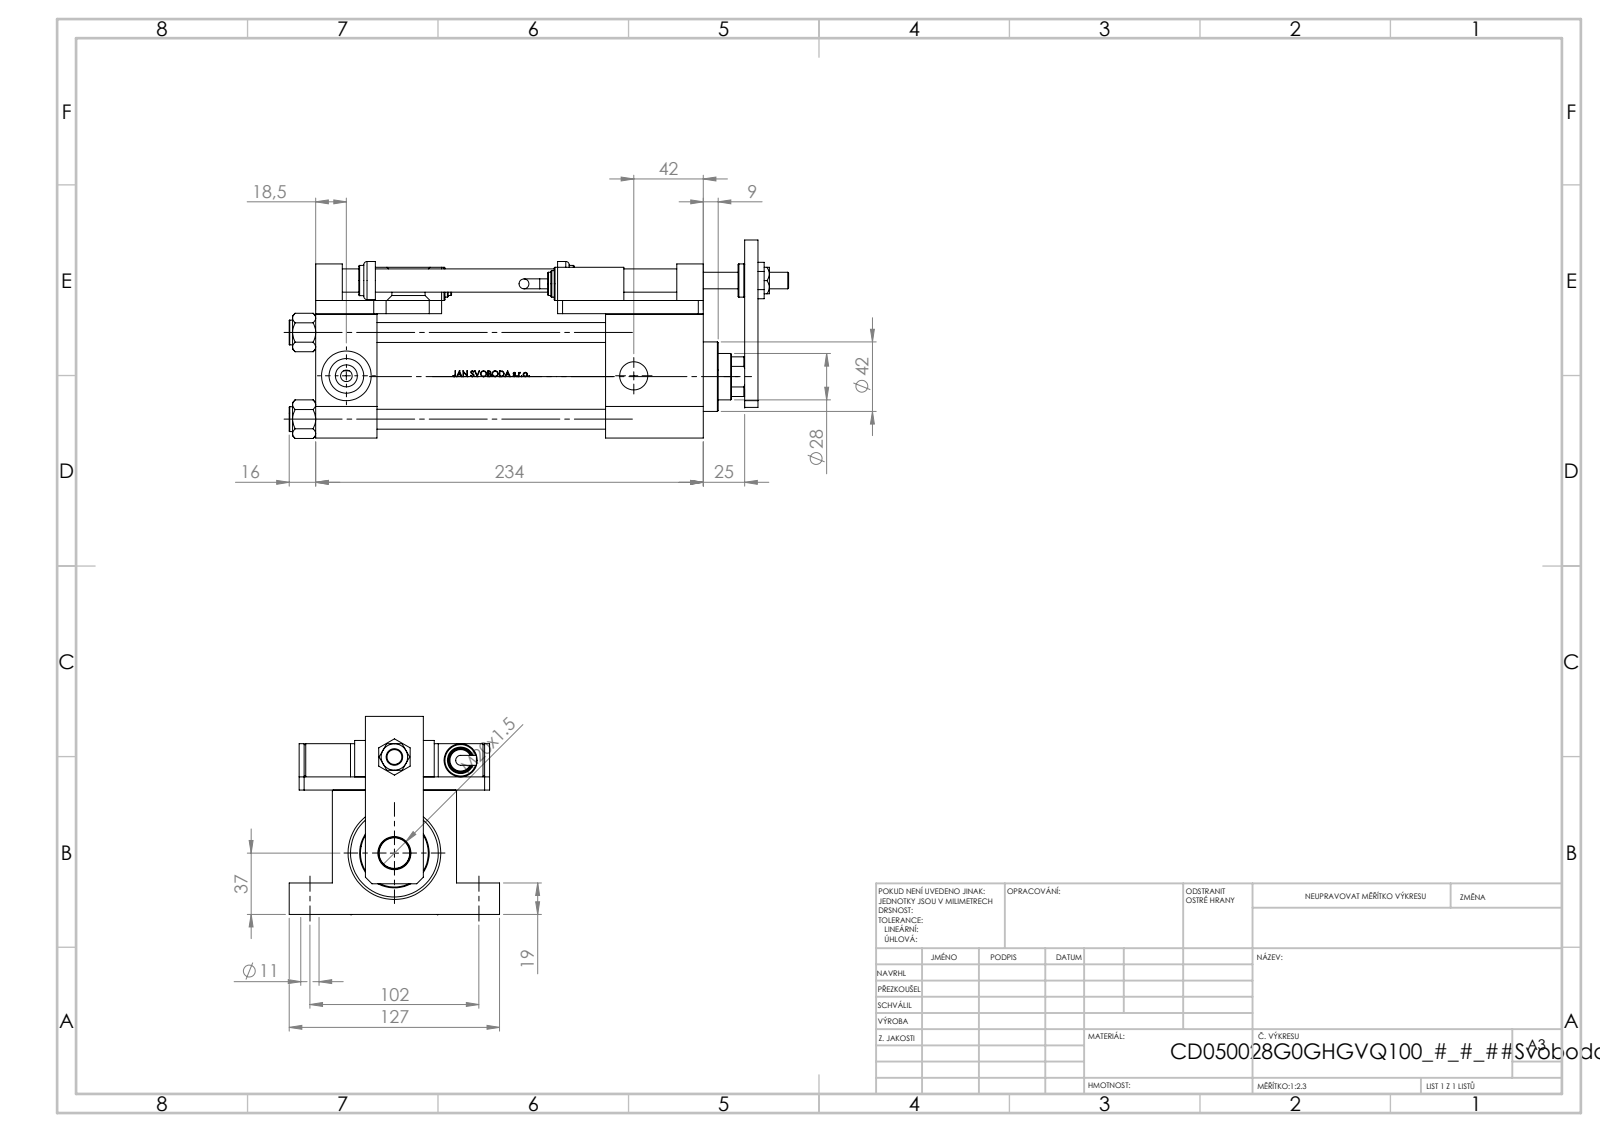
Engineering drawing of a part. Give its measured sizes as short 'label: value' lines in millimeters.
name: V215CD_SWITCH_Q_PODLOZKA_BACK; V215CD_SWITCH_Q_DIMA; V215CD_SWITCH_Q_SWITCH; V215CD_SWITCH_Q_NUT (+7 more)
written by: SolidWorks 2019 (CONFIG_CONTROL_DESIGN)
unit: mm
bodies: 24 solids, 1315 faces (552 planar, 192 cylindrical, 571 other)
size: 301.5 × 127 × 119.77
volume: 1 163 000 mm³; area: 295 317 mm²
holes: 4× ⌀8.5, 4× ⌀11, 4× ⌀12, 4× ⌀13.5, 2× ⌀7, 2× ⌀14, 2× ⌀20.96, 1× ⌀10, 1× ⌀17, 1× ⌀18.5, 1× ⌀20, 1× ⌀28
bosses: 4× ⌀15, 3× ⌀20, 2× ⌀16, 2× ⌀14, 2× ⌀6, 1× ⌀56, 1× ⌀42, 1× ⌀23
rounds: 4× R7.5, 1× R13.5
face distances: 8, 75, 83, 20, 37, 234, 197, 84, 59, 19
hole spacings: 40.82, 52.3, 32, 35.36, 36.63, 37.34, 40.44, 67.19
